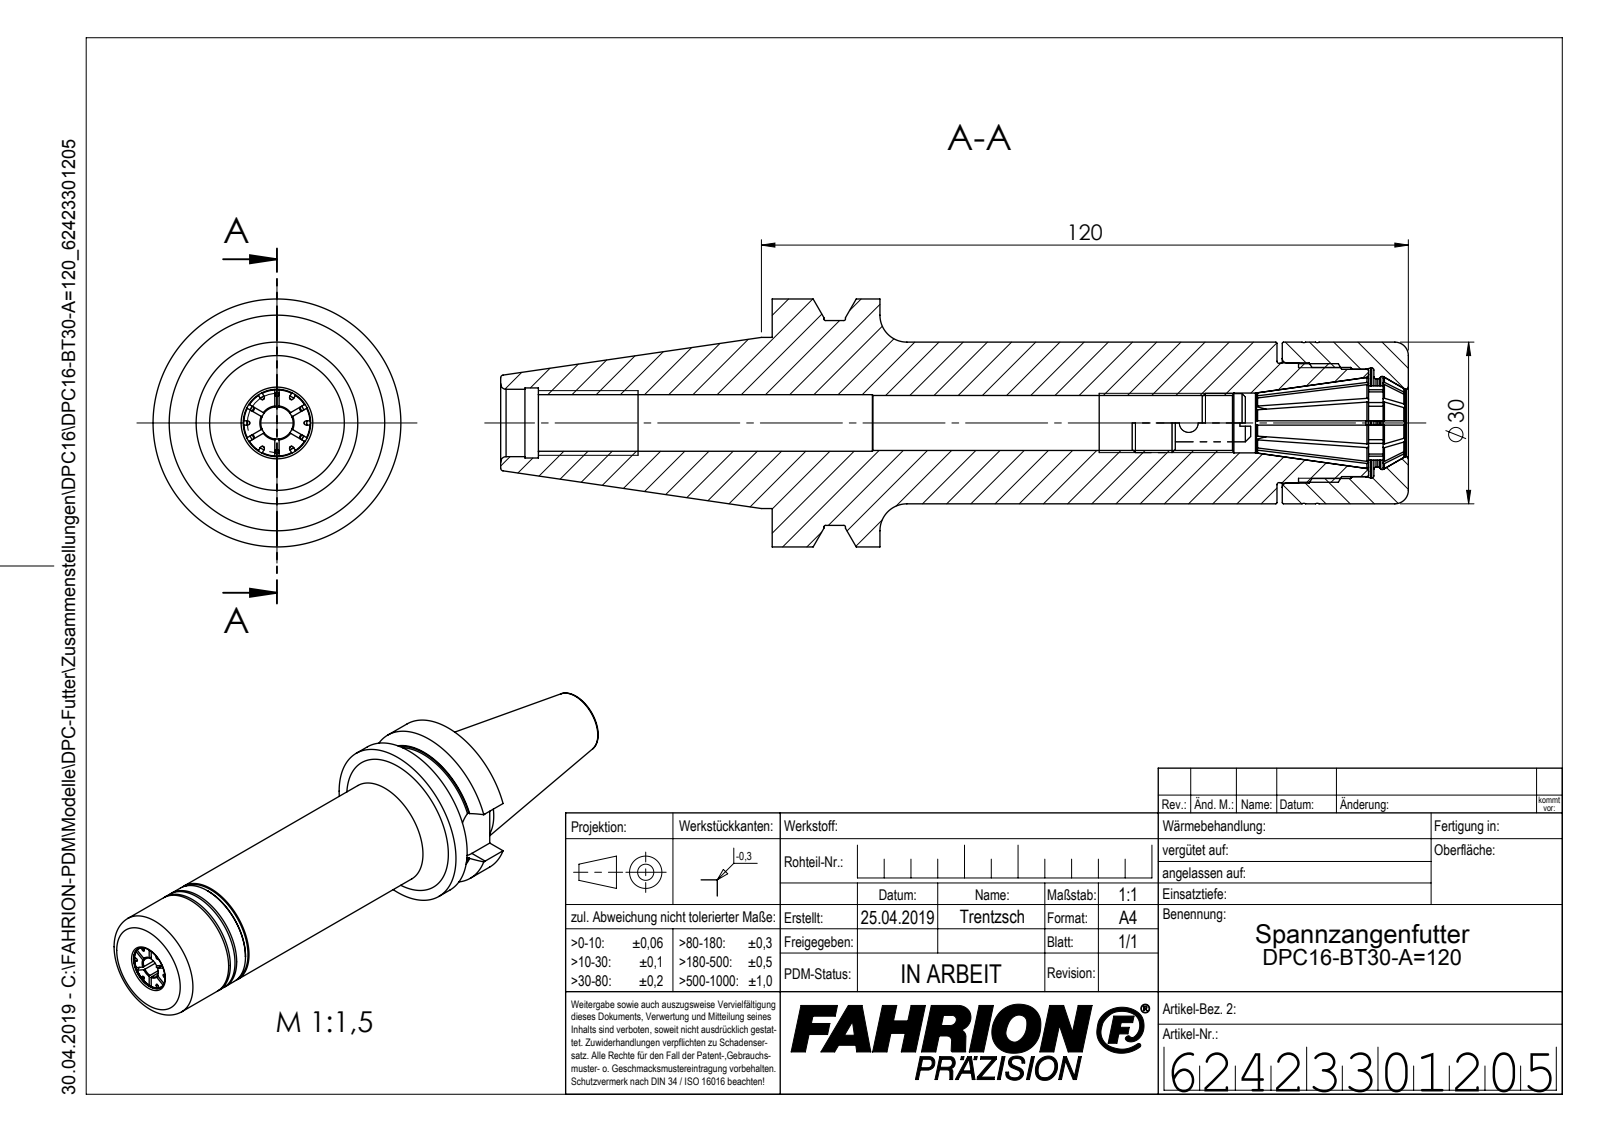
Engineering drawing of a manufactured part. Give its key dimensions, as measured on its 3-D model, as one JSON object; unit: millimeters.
{"part_name": "13001_B=6; DPC16_6380300; 44363951200; DPC16-BT30-A=120", "step_written_by": "SolidWorks 2020 (AUTOMOTIVE_DESIGN)", "units": "millimeters", "bodies": {"solids": 3, "faces": 325, "planar": 81, "cylindrical": 73, "other": 171}, "overall_size": [168.4, 46, 46], "volume_mm3": 108629, "surface_area_mm2": 31946, "round_holes": [[6, 1], [10.2, 1], [10.5, 1], [11.1, 1], [12.5, 1], [13, 1], [16.4, 1], [19.93, 1], [20.42, 1], [20.6, 1], [22.32, 1]], "round_bosses_or_shafts": [[46, 1], [38, 1], [31.75, 1], [30, 1], [22.3, 1], [22, 1], [19.9, 1], [16.97, 1]], "partial_cylinders_radius": [[6.9, 1], [8.05, 1]], "face_to_face_distances": [0.8, 15.9, 16.7, 20, 98, 118, 0.98, 93.62, 73.62, 24.38]}
